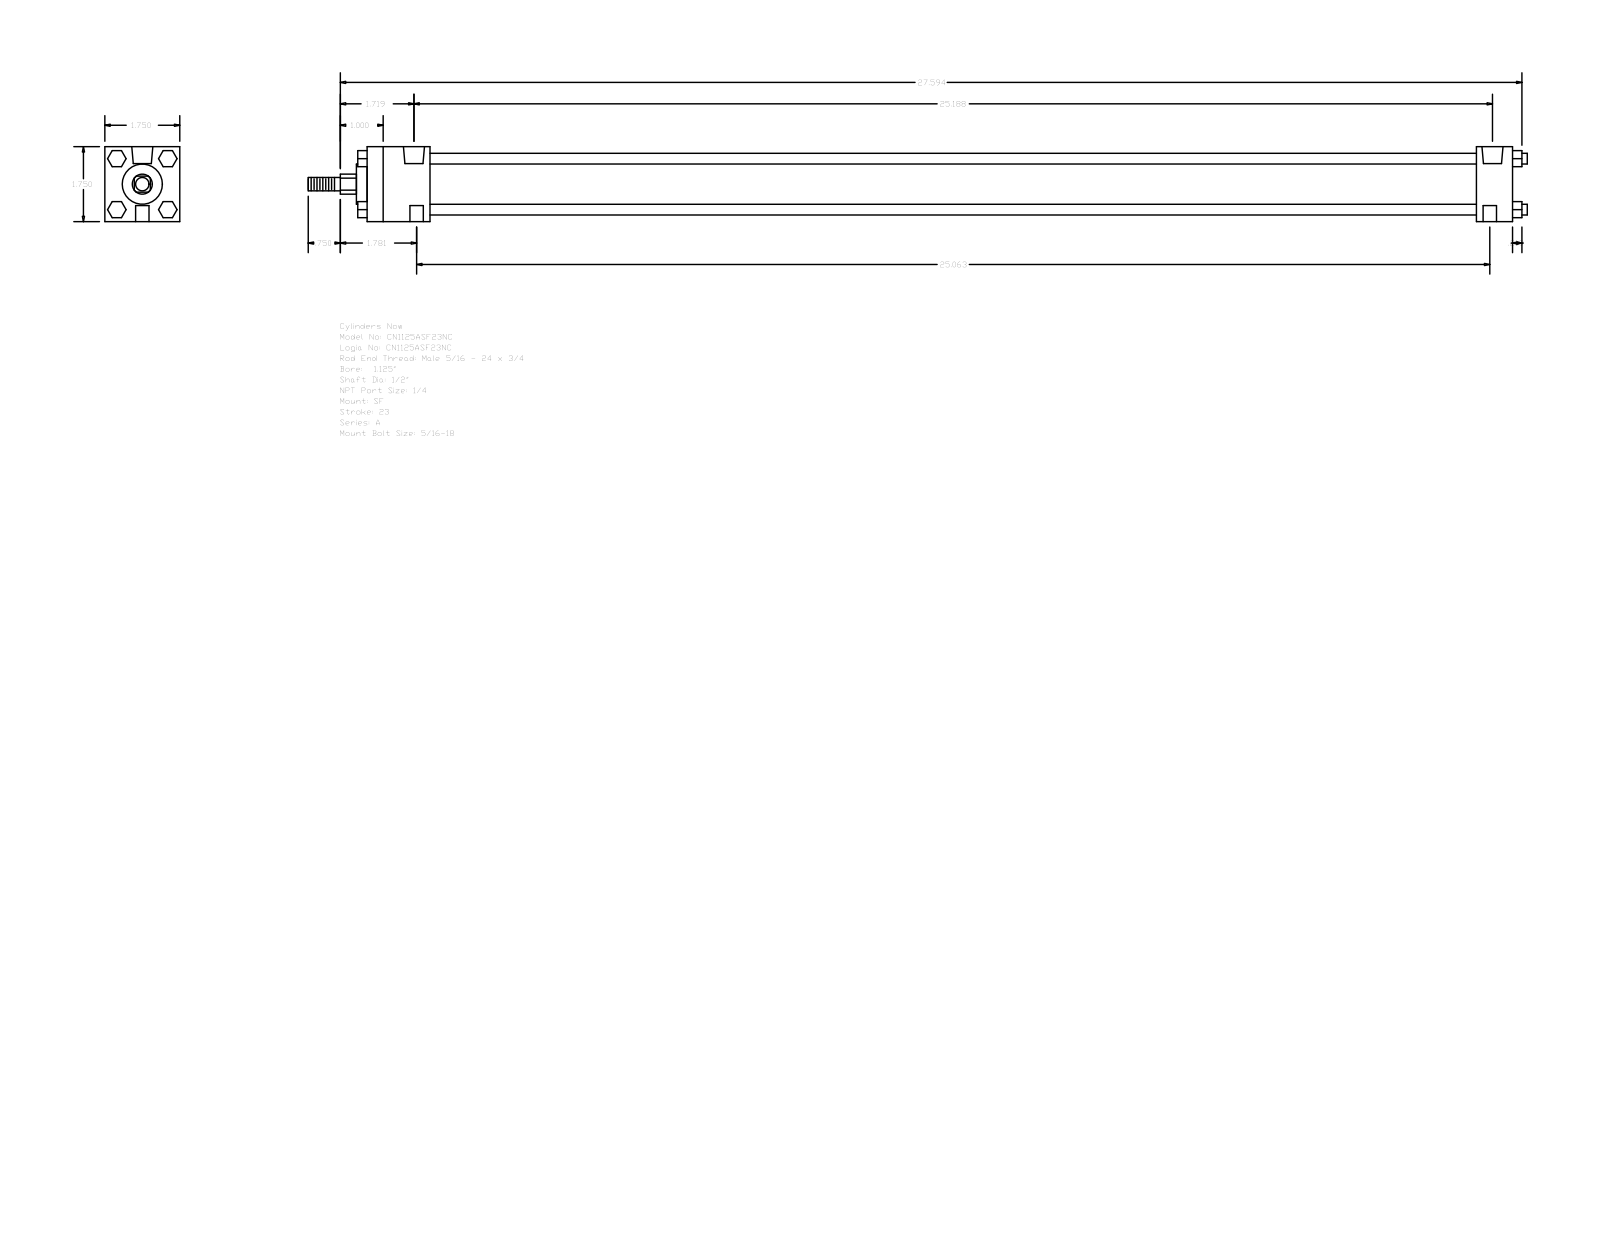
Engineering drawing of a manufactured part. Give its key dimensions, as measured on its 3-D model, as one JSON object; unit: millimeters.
{"part_name": "A_SF__0112_0.5", "step_written_by": "GSSL Pune (CONFIG_CONTROL_DESIGN)", "units": "millimeters", "bodies": {"solids": 0, "faces": 120, "planar": 92, "cylindrical": 28, "other": 0}, "overall_size": [723.11, 44.45, 44.45], "round_holes": [[5.56, 2], [7.94, 2], [12.49, 2]], "round_bosses_or_shafts": [[6.35, 4], [31.88, 1], [23.81, 1], [12.7, 1], [7.94, 1]], "partial_cylinders_radius": [[5.94, 1]], "face_to_face_distances": [44.46, 679.45, 658.01, 21.44, 37.3, 620.71, 642.15, 9.53, 5.59, 26.99], "hole_center_spacings": [636.59, 1.58, 1.59, 638.17, 638.18, 639.76]}
